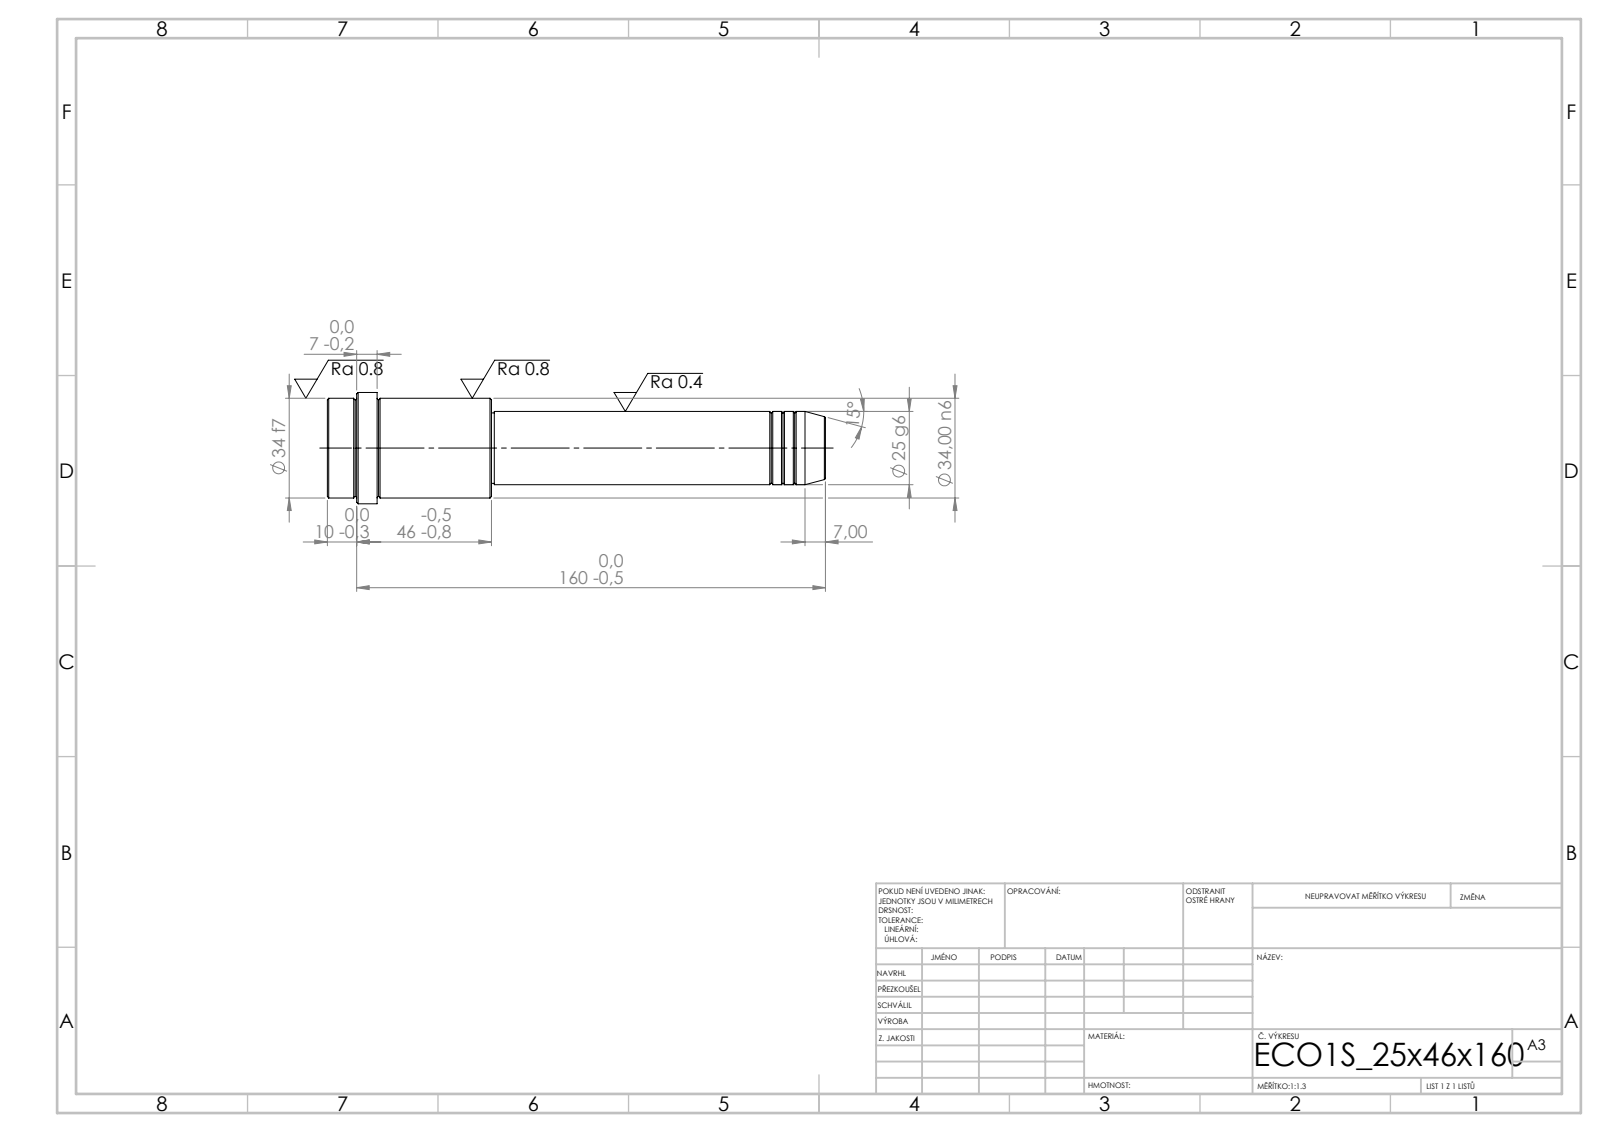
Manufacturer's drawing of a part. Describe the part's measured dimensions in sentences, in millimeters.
Its 3-D file was written by "SolidWorks 2019 (CONFIG_CONTROL_DESIGN)". It is 1 solid with 52 faces: 6 planar, 16 cylindrical and 30 other. Overall it measures 170 by 38 by 38 millimeters. Its volume is 107 641 cubic millimeters and its surface area 17 340 square millimeters. Round bosses or shafts: 1 of diameter 38, 1 of diameter 34, 1 of diameter 25, 1 of diameter 24. The main face-to-face distances are 56, 114, 170, 153, 39, 17, 160, 46, 7, 10.
